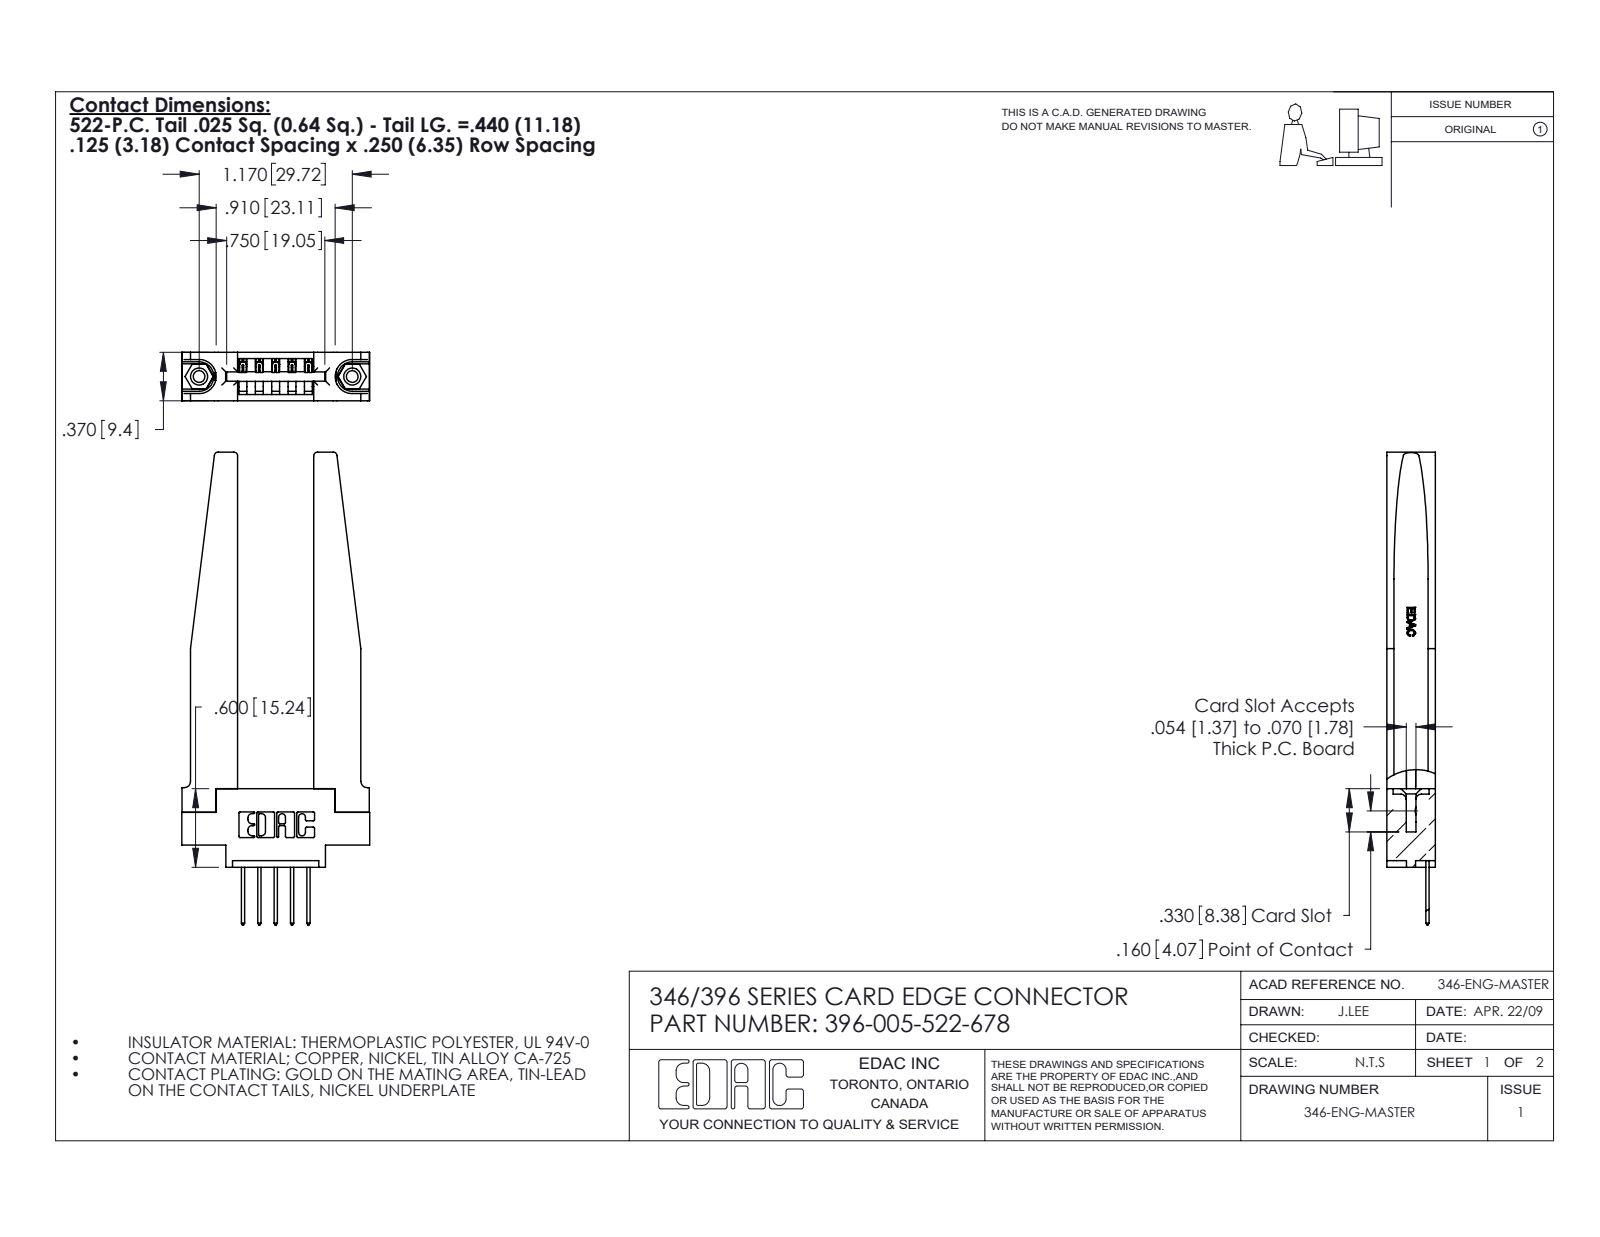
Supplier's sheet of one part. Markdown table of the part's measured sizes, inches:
| quantity | value |
| --- | --- |
| part name | 346-220-078_345-220-078; 345-250-001_345-250-001-102; 345-292-001_345-293-122; 396-005-522-678 (+1 more) |
| STEP written by | SolidWorks 2020 (CONFIG_CONTROL_DESIGN) |
| units | inches |
| bodies | 10 solids, 664 faces (436 planar, 176 cylindrical, 52 other) |
| overall size | 3.61 × 1.435 × 0.37 |
| volume | 0.608 in³ |
| surface area | 15.78 in² |
| round holes (diameter × count) | 0.089 × 2, 0.125 × 2, 0.156 × 2, 0.064 × 1 |
| round bosses / shafts (diameter × count) | 0.155 × 2 |
| partial cylindrical surfaces (radius × count) | 0.01 × 22, 0.006 × 10, 0.01 × 10, 0.03 × 8, 0.007 × 6, 0.031 × 6, 0.026 × 3, 0.031 × 2 |
| main face-to-face distances | 0.37, 0.15, 0.22, 0.581, 0.25, 0.072, 0.148, 0.102, 0.048, 0.322 |
| hole center spacings | 0.246, 0.969, 1.17 |
